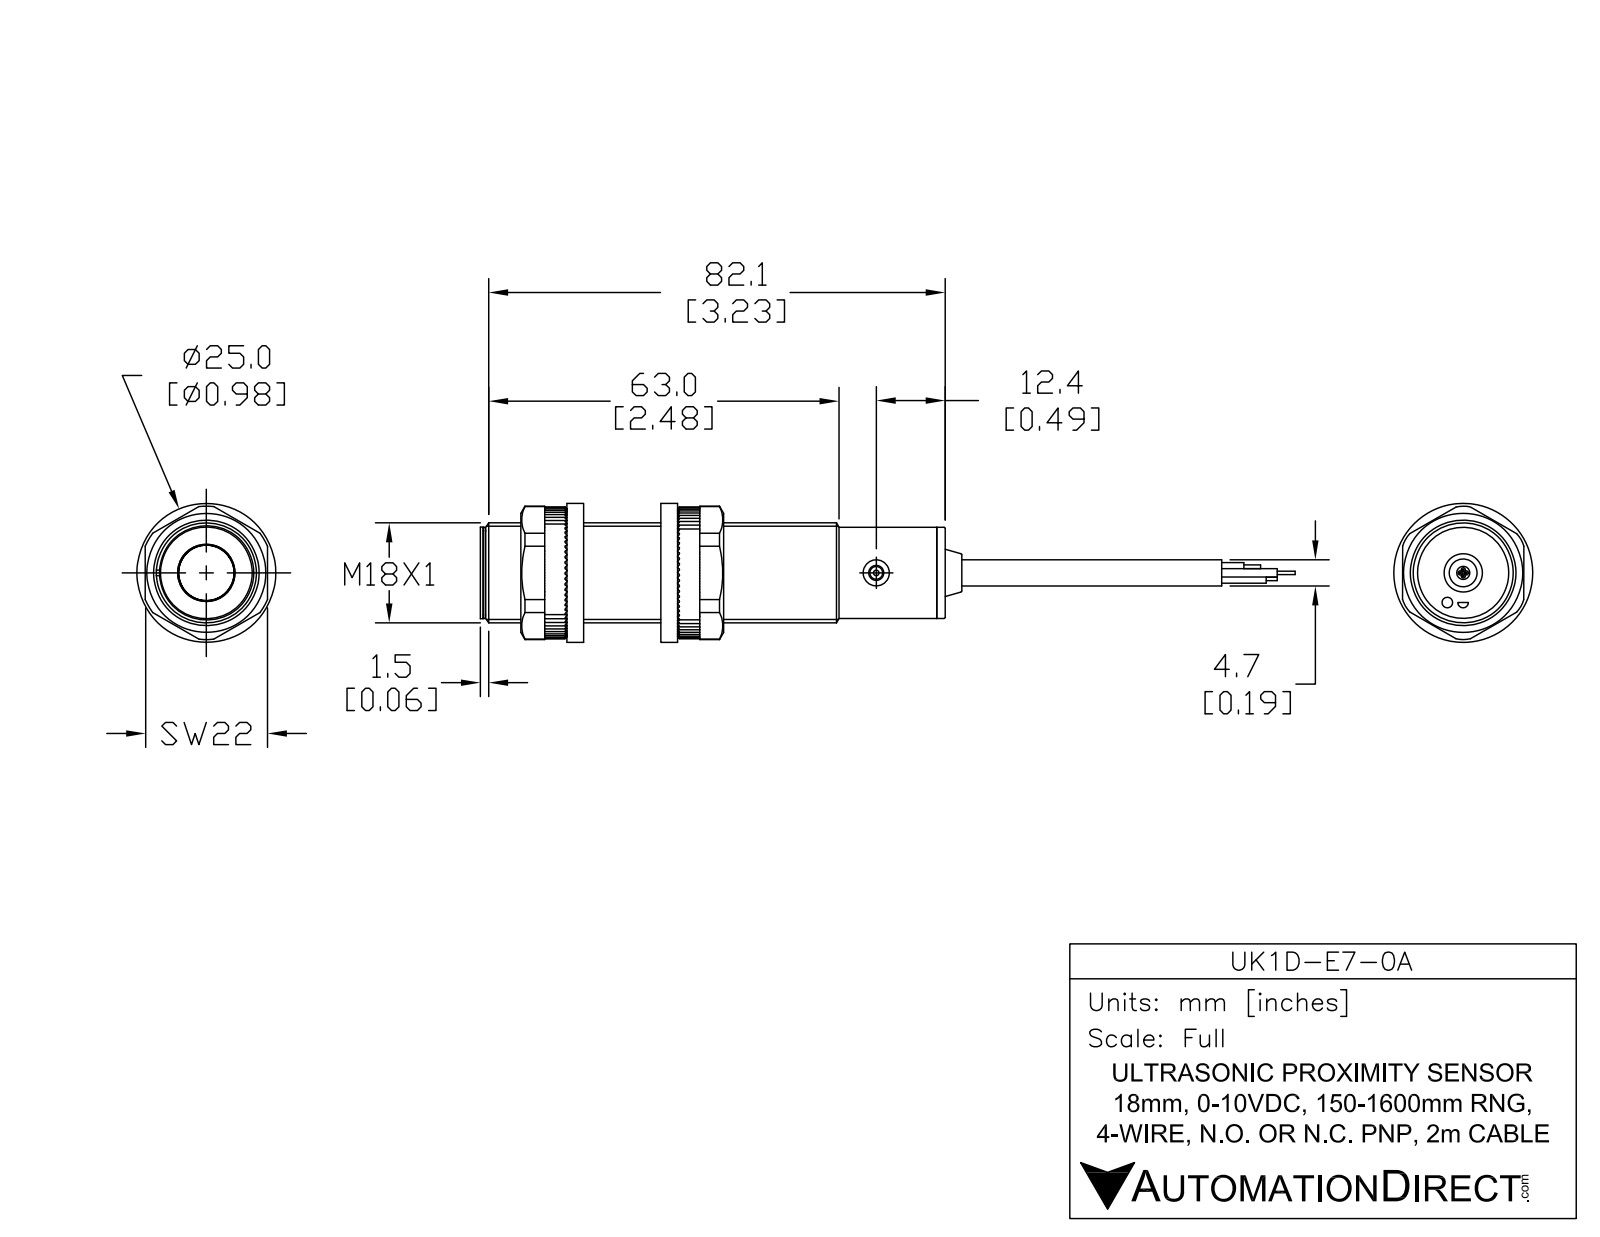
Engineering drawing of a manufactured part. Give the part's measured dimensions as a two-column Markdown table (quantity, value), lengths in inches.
| quantity | value |
| --- | --- |
| part name | UK1D-E7-0A |
| STEP written by | SolidWorks 2017 (AUTOMOTIVE_DESIGN) |
| units | inches |
| bodies | 6 solids, 55 faces (17 planar, 24 cylindrical, 14 other) |
| overall size | 4.832 × 0.709 × 0.709 |
| volume | 1.285 in³ |
| surface area | 10.69 in² |
| round holes (diameter × count) | 0.185 × 2, 0.106 × 1 |
| round bosses / shafts (diameter × count) | 0.709 × 1, 0.646 × 1, 0.622 × 1, 0.374 × 1, 0.189 × 1, 0.091 × 1 |
| main face-to-face distances | 3.193, 3.252, 0.059, 0.039, 3.232, 3.291, 0.041, 3.234, 3.293, 3.257 |
